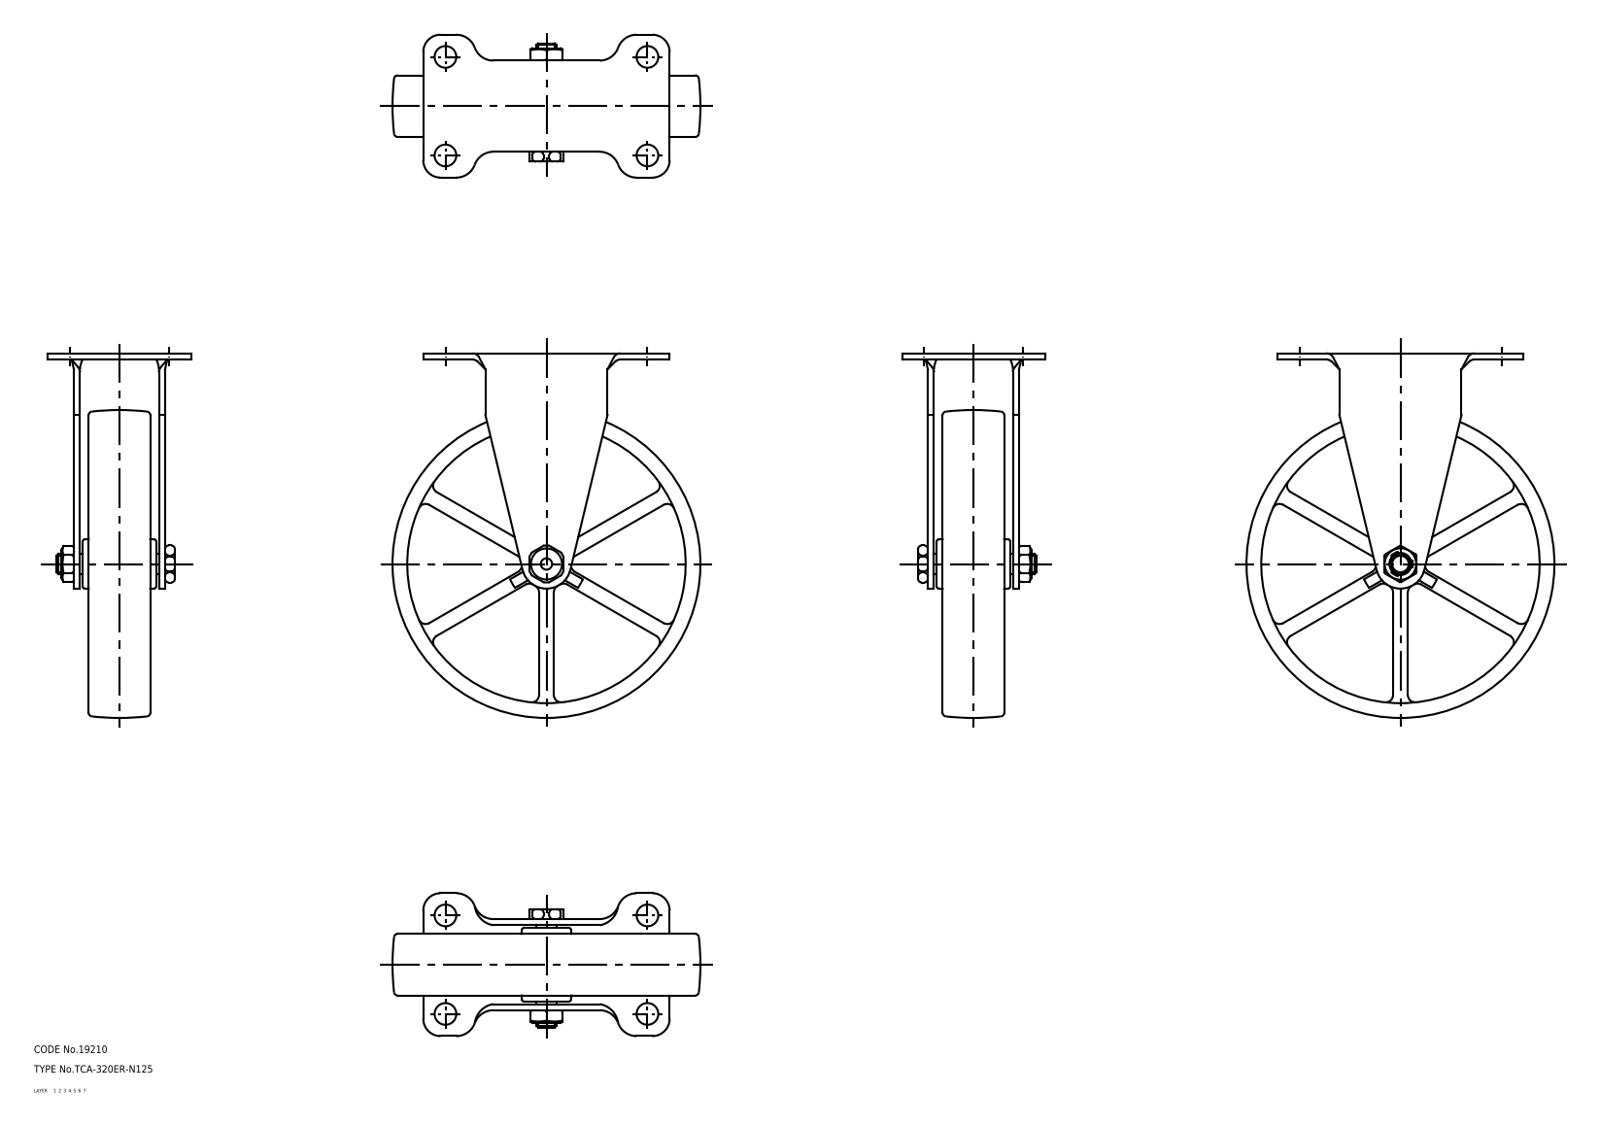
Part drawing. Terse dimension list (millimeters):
name: wheel; axle; 320ER_N125_2878_36
written by: CADfix (AUTOMOTIVE_DESIGN)
unit: mm
bodies: 3 solids, 495 faces (0 planar, 0 cylindrical, 495 other)
size: 148 × 125 × 58
volume: 246 229 mm³; area: 65 165 mm²
